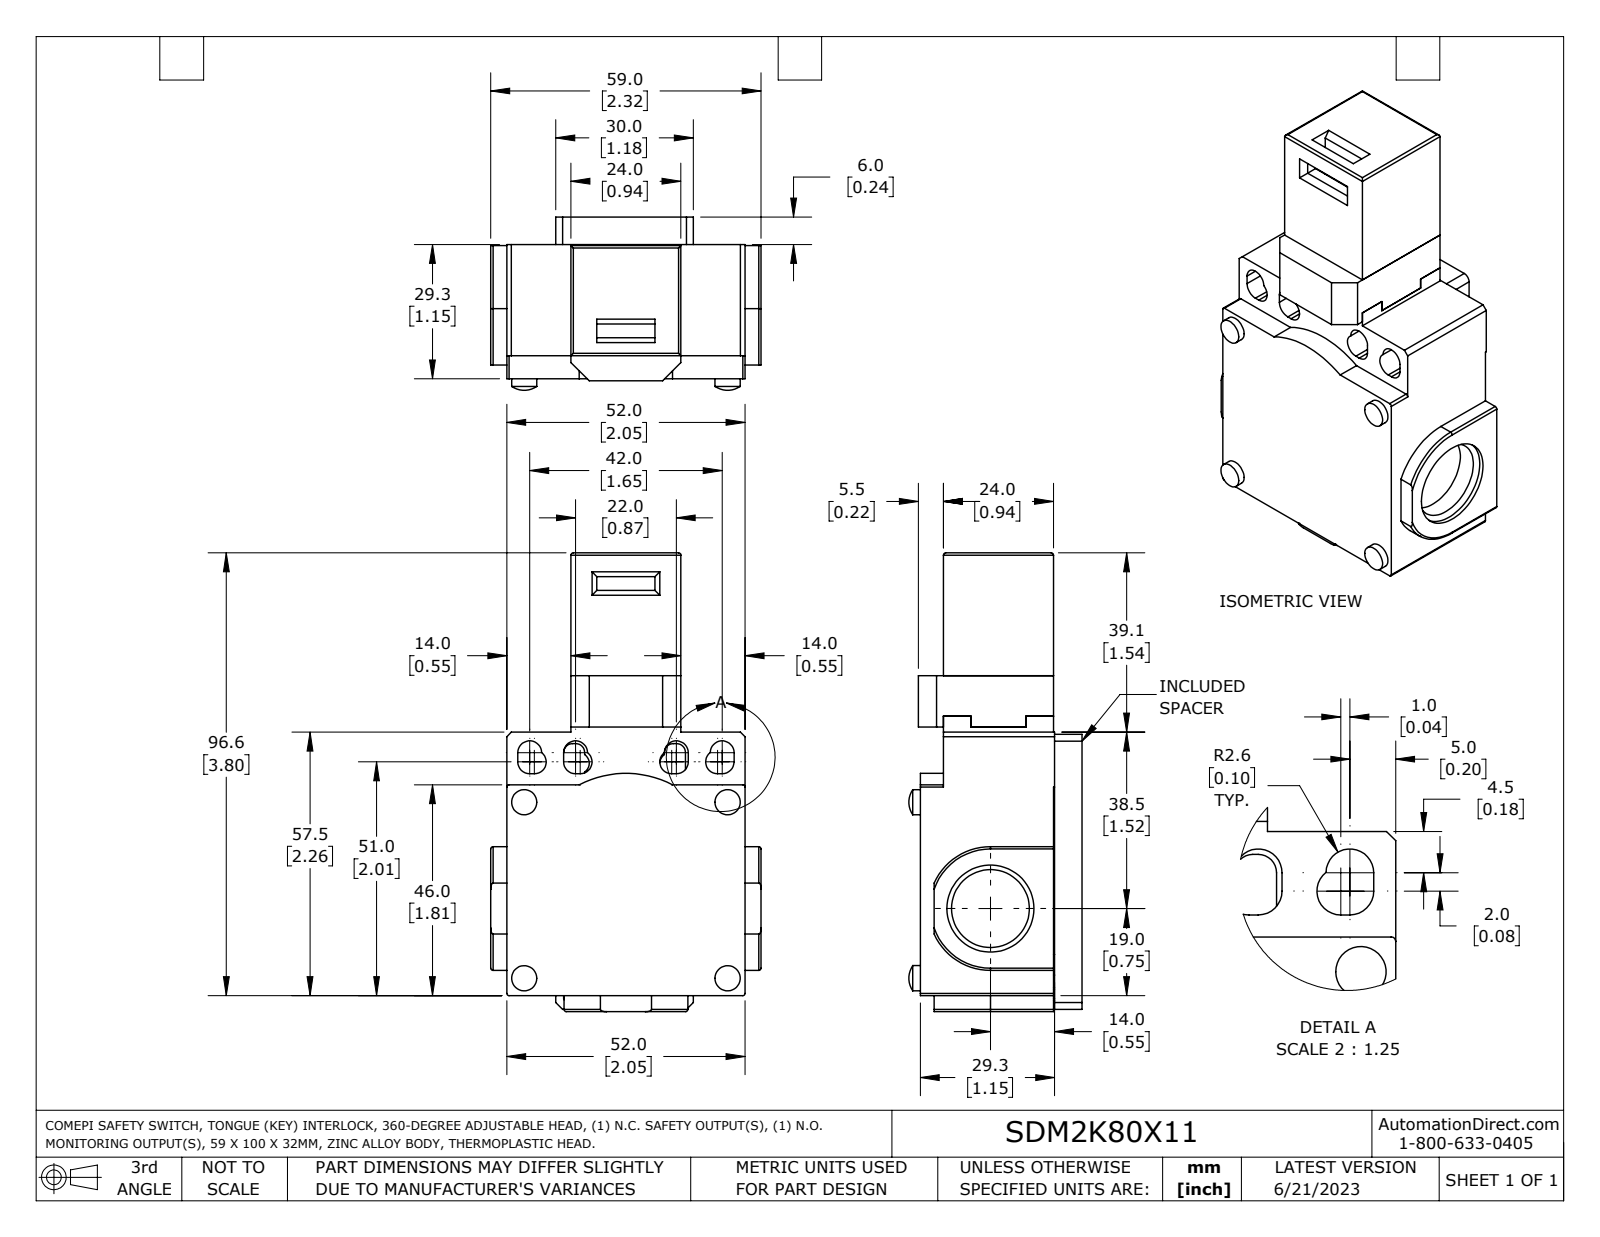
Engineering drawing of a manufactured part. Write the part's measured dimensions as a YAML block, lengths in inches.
part_name: "SDM2K80X11"
step_written_by: "SolidWorks 2021 (AUTOMOTIVE_DESIGN)"
units: inches
bodies: {solids: 6, faces: 307, planar: 178, cylindrical: 113, other: 16}
overall_size: [3.941, 2.323, 1.488]
volume: 6.706
surface_area: 45.71
round_holes:
  - {diameter: 0.669, count: 2}
  - {diameter: 0.748, count: 2}
  - {diameter: 0.591, count: 1}
round_bosses_or_shafts:
  - {diameter: 0.217, count: 4}
partial_cylinders:
  - {radius: 0.016, count: 24}
  - {radius: 0.079, count: 24}
  - {radius: 0.02, count: 14}
  - {radius: 0.102, count: 12}
  - {radius: 0.059, count: 2}
  - {radius: 0.091, count: 2}
  - {radius: 0.531, count: 2}
  - {radius: 0.394, count: 1}
face_to_face_distances: [0.551, 1.144, 1.496, 0.945, 0.236, 0.138, 1.154, 0.199, 0.955, 0.079]
hole_center_spacings: [0.069]
